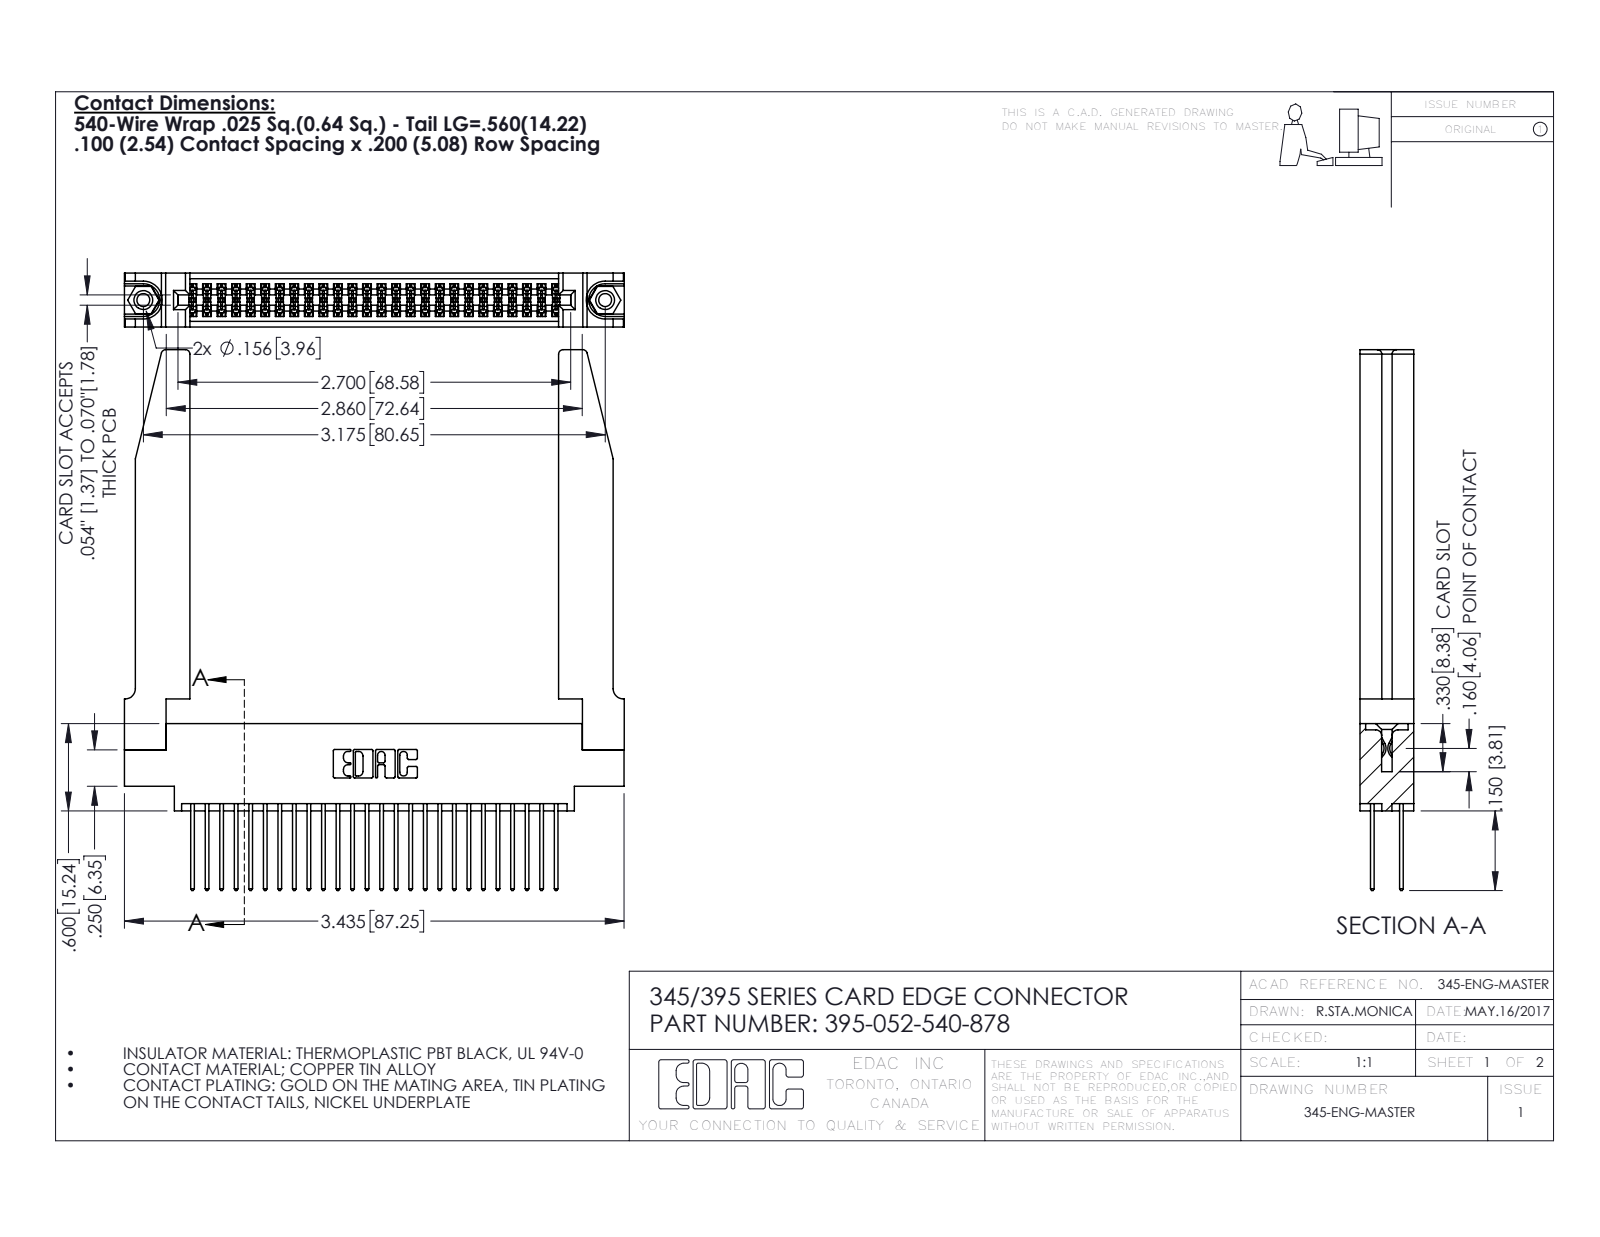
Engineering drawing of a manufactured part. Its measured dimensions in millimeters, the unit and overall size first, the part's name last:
Units: millimetres
Overall size (bounding box): 94.4 × 87.3 × 9.4
Round holes (diameter × count): ⌀2.3 ×2, ⌀3.2 ×2, ⌀4 ×2, ⌀1.6 ×1
Round bosses / shafts (diameter × count): ⌀3.9 ×2
Partial cylindrical surfaces — rounded edges, fillets, slot ends (radius × count): R0.2 ×78, R0.3 ×52, R0.3 ×22, R0.8 ×8, R0.2 ×6, R0.8 ×6, R0.7 ×3, R0.4 ×2
Main face-to-face distances: 9.4, 1.8, 7.6, 2.5, 6.9, 0.6, 5.1, 5.7, 4.4, 3.8
Hole centre spacings: 6.9, 74.7, 80.6
Volume: 16 200 mm³ · Surface area: 20 030 mm²
Bodies: 57 solids, 2964 faces (1942 planar, 970 cylindrical, 52 other)
Part name (STEP PRODUCT): 395-052-540-878; 345-220-078_345-220-078; 345-292-001_345-293-140; 345-250-001_345-250-001-102 (+1 more)
STEP written by: SolidWorks 2016 (CONFIG_CONTROL_DESIGN)
